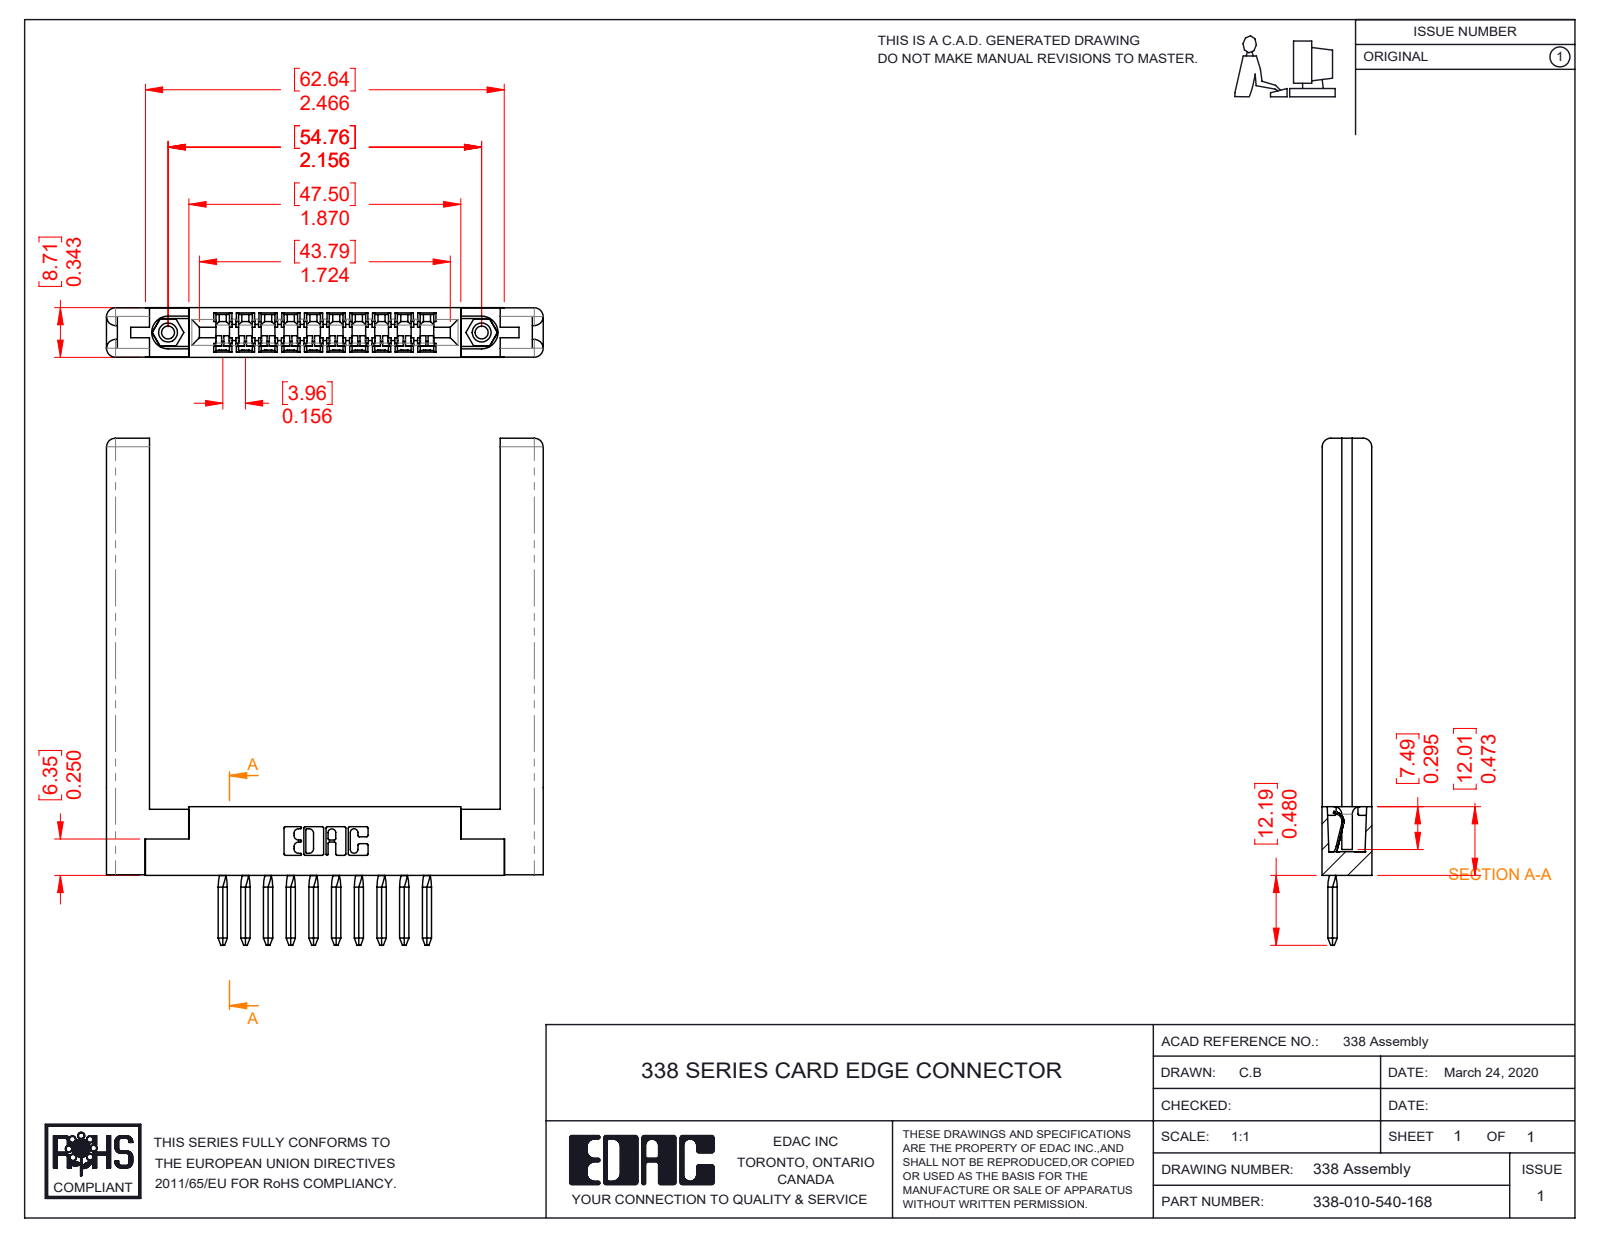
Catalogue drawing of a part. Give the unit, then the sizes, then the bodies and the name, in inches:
Units: inches
Overall size (bounding box): 3.485 × 3.002 × 0.343
Round holes (diameter × count): ⌀0.089 ×2, ⌀0.125 ×2, ⌀0.156 ×2
Round bosses / shafts (diameter × count): ⌀0.155 ×2
Partial cylindrical surfaces — rounded edges, fillets, slot ends (radius × count): R0.025 ×42, R0.01 ×22, R0.008 ×10, R0.055 ×8, R0.061 ×8, R0.067 ×8, R0.1 ×8, R0.007 ×6
Main face-to-face distances: 0.341, 0.34, 0.136, 0.207, 0.134, 0.206, 0.343, 2.412, 0.071, 0.22
Hole centre spacings: 2.156
Volume: 0.783 in³ · Surface area: 19.9 in²
Bodies: 15 solids, 1166 faces (784 planar, 318 cylindrical, 64 other)
Part name (STEP PRODUCT): 338-010-540-168; 307-220-058; 345-250-001_345-250-001-102; 338-290-001_540 (+1 more)
STEP written by: SolidWorks 2016 (CONFIG_CONTROL_DESIGN)
